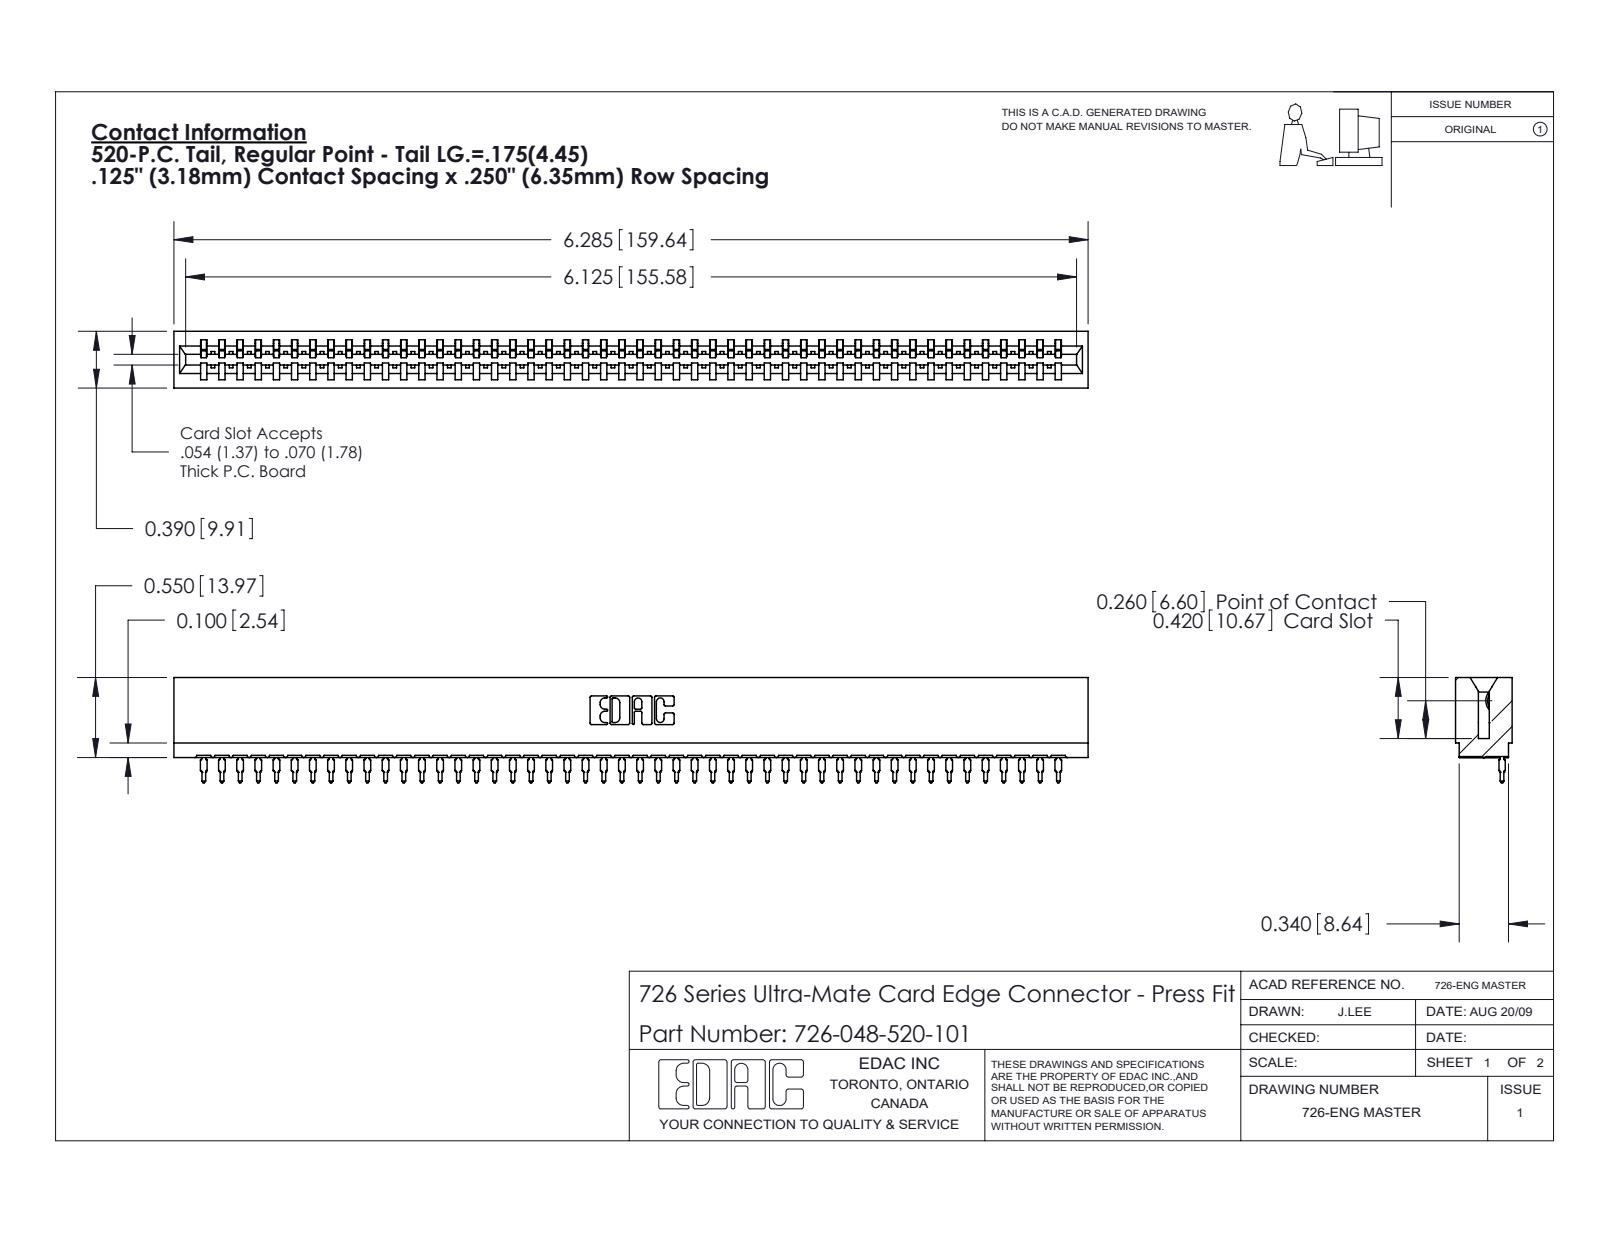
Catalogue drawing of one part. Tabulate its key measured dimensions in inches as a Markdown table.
| quantity | value |
| --- | --- |
| part name | 726 Part_.515 Slot Depth - 01; 726-048-520-101; 746-292-001_520 |
| STEP written by | SolidWorks 2020 (CONFIG_CONTROL_DESIGN) |
| units | inches |
| bodies | 49 solids, 5281 faces (3079 planar, 954 cylindrical, 1248 other) |
| overall size | 6.285 × 0.724 × 0.39 |
| volume | 0.863 in³ |
| surface area | 33.09 in² |
| partial cylindrical surfaces (radius × count) | 0.021 × 96, 0.015 × 49, 0.01 × 22, 0.007 × 6, 0.031 × 6, 0.005 × 4, 0.011 × 4, 0.026 × 3 |
| main face-to-face distances | 0.057, 0.333, 0.39, 0.025, 0.307, 0.25, 0.275, 0.365, 0.032, 0.174 |
